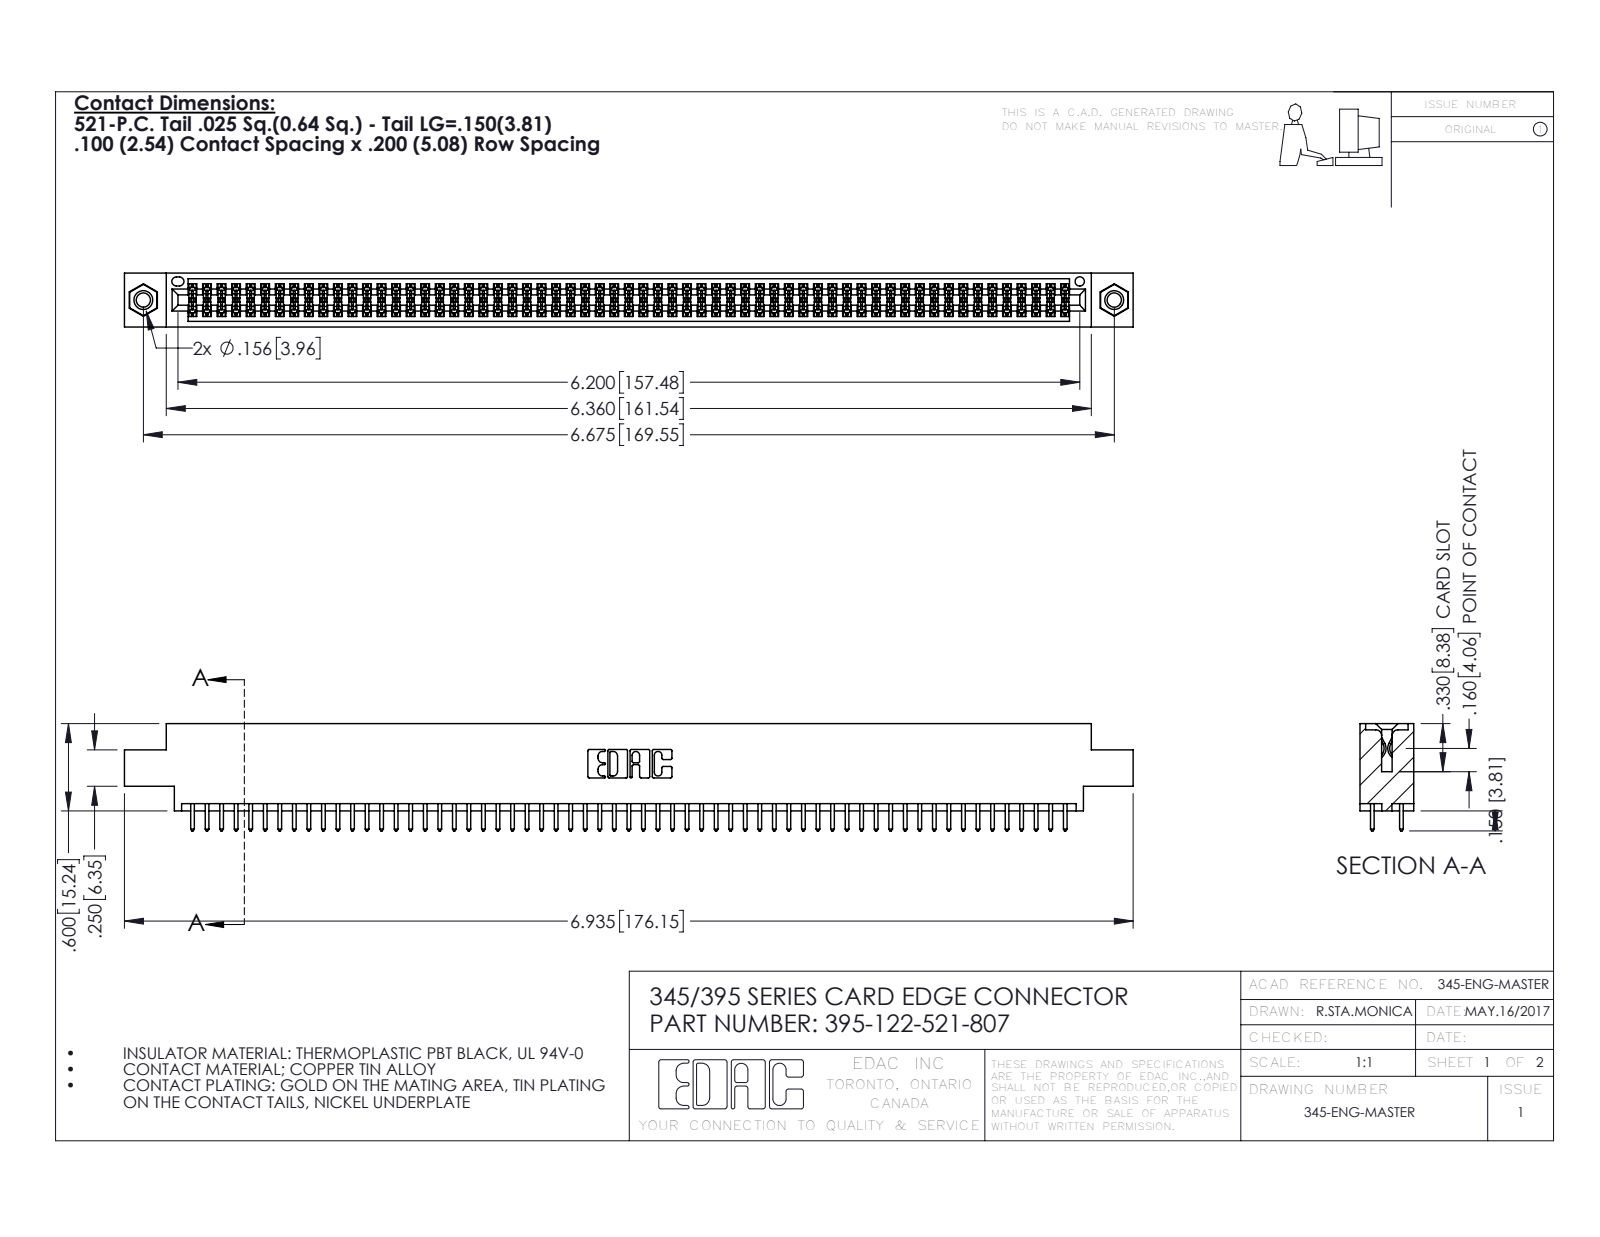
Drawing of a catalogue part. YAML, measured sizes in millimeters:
part_name: "395-122-521-807; 345 Part_0.170 Offset - 0.156 Dia-TI; 345-250-001_345-250-005-103; 345-292-001_345-293-121"
step_written_by: "SolidWorks 2016 (CONFIG_CONTROL_DESIGN)"
units: millimeters
bodies: {solids: 125, faces: 6290, planar: 4142, cylindrical: 2132, other: 16}
overall_size: [176.1, 18.7, 9.4]
volume: 17110
surface_area: 25510
round_holes:
  - {diameter: 2.5, count: 2}
  - {diameter: 3.2, count: 2}
  - {diameter: 4, count: 2}
  - {diameter: 1.6, count: 1}
round_bosses_or_shafts:
  - {diameter: 3.9, count: 2}
partial_cylinders:
  - {radius: 0.2, count: 183}
  - {radius: 0.3, count: 122}
  - {radius: 0.3, count: 22}
  - {radius: 0.2, count: 6}
  - {radius: 0.8, count: 6}
  - {radius: 0.7, count: 3}
  - {radius: 0.4, count: 2}
  - {radius: 0.5, count: 2}
face_to_face_distances: [1.8, 7.6, 5.1, 9.4, 2.5, 6.9, 0.6, 5.7, 4.4, 3.8]
hole_center_spacings: [6.9, 163.6, 169.5]
